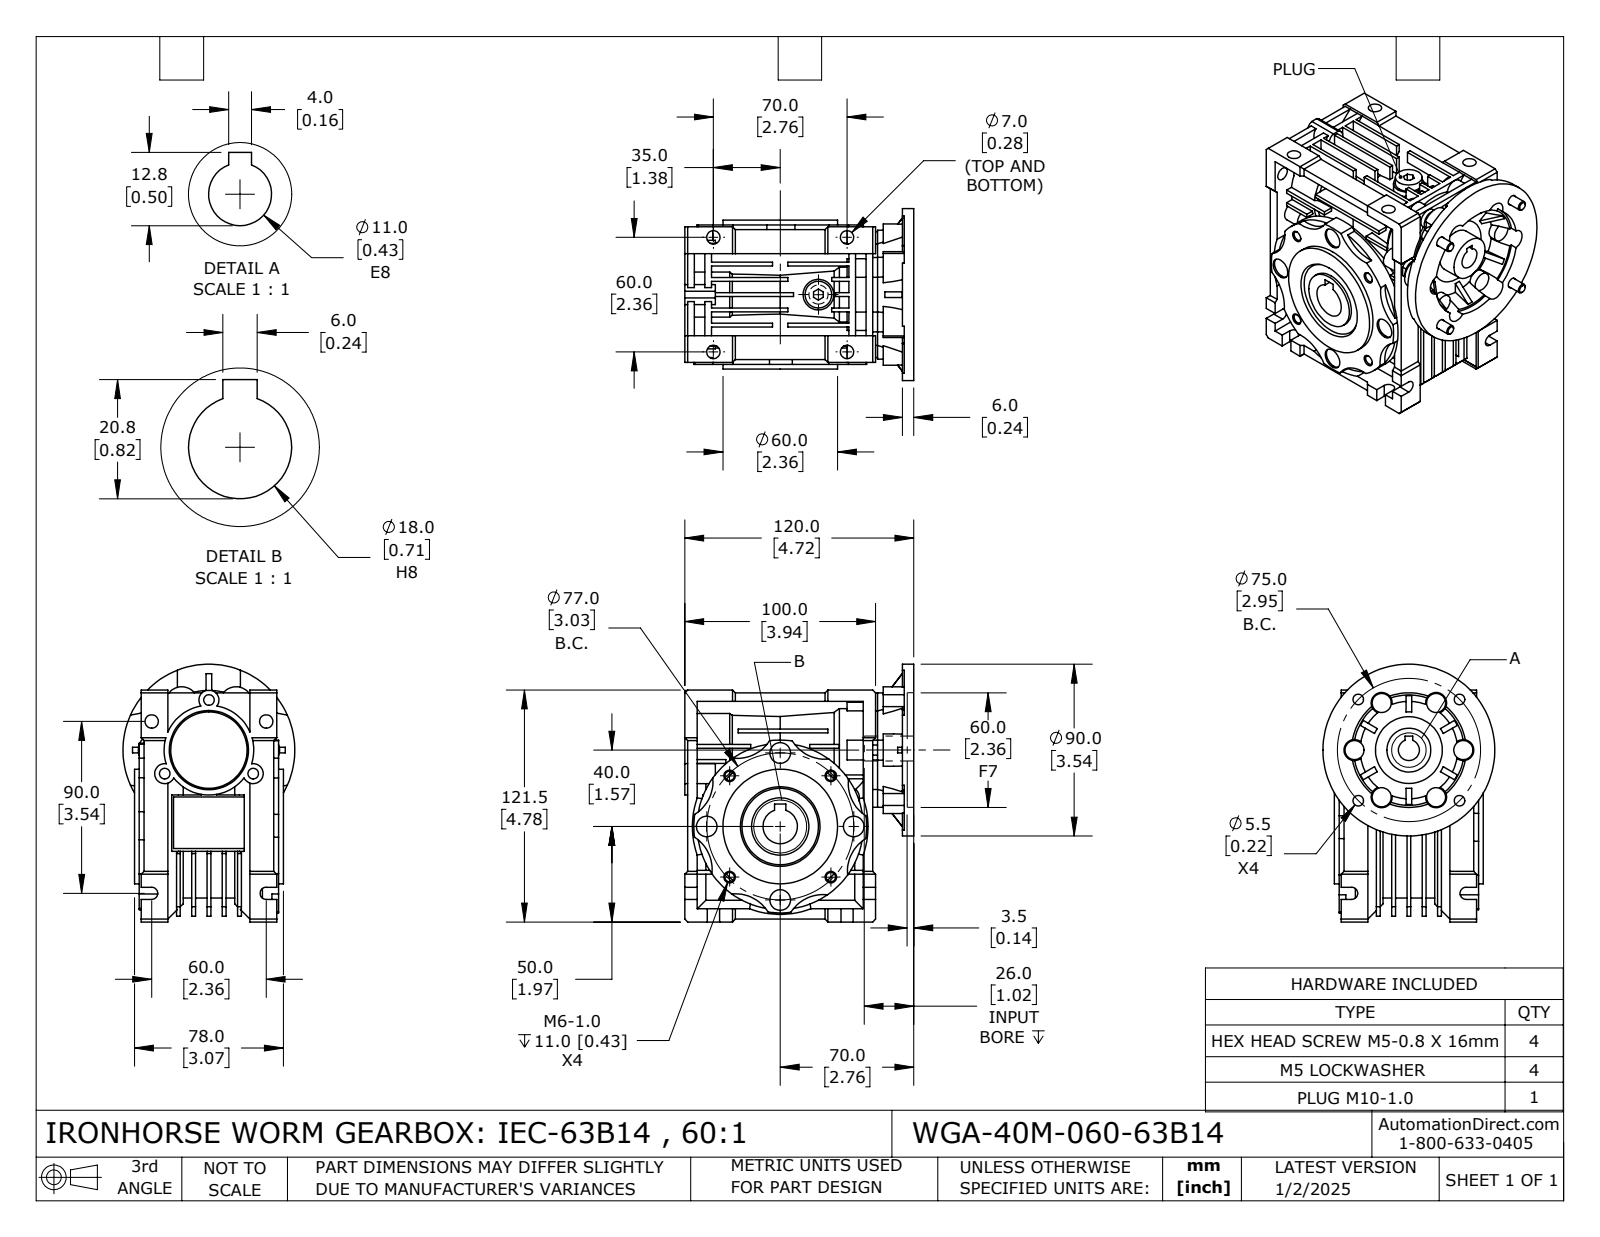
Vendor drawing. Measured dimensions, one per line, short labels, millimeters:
name: WGA-40M-060-63B14
written by: SolidWorks 2024 (CONFIG_CONTROL_DESIGN)
unit: mm
bodies: 14 solids, 1003 faces (564 planar, 307 cylindrical, 132 other)
size: 135 × 127.7 × 90
volume: 667 307 mm³; area: 163 100 mm²
holes: 6× ⌀7, 4× ⌀4.92, 4× ⌀5.1, 4× ⌀5.5, 4× ⌀10.8, 3× ⌀5.55, 1× ⌀9, 1× ⌀11, 1× ⌀11.5, 1× ⌀18, 1× ⌀23, 1× ⌀28
bosses: 6× ⌀10, 4× ⌀9.2, 4× ⌀5, 1× ⌀90, 1× ⌀75, 1× ⌀60, 1× ⌀54, 1× ⌀47
rounds: 9× R5.25, 8× R20, 6× R3.2, 6× R5.22, 6× R5.5, 6× R8.5, 4× R5.51, 1× R30
face distances: 8, 6, 2, 1.5, 16, 10, 5, 14, 2.5, 19
hole spacings: 29.1, 37.5, 53.04, 70.22, 33.54, 38.5, 54.45, 75.01
